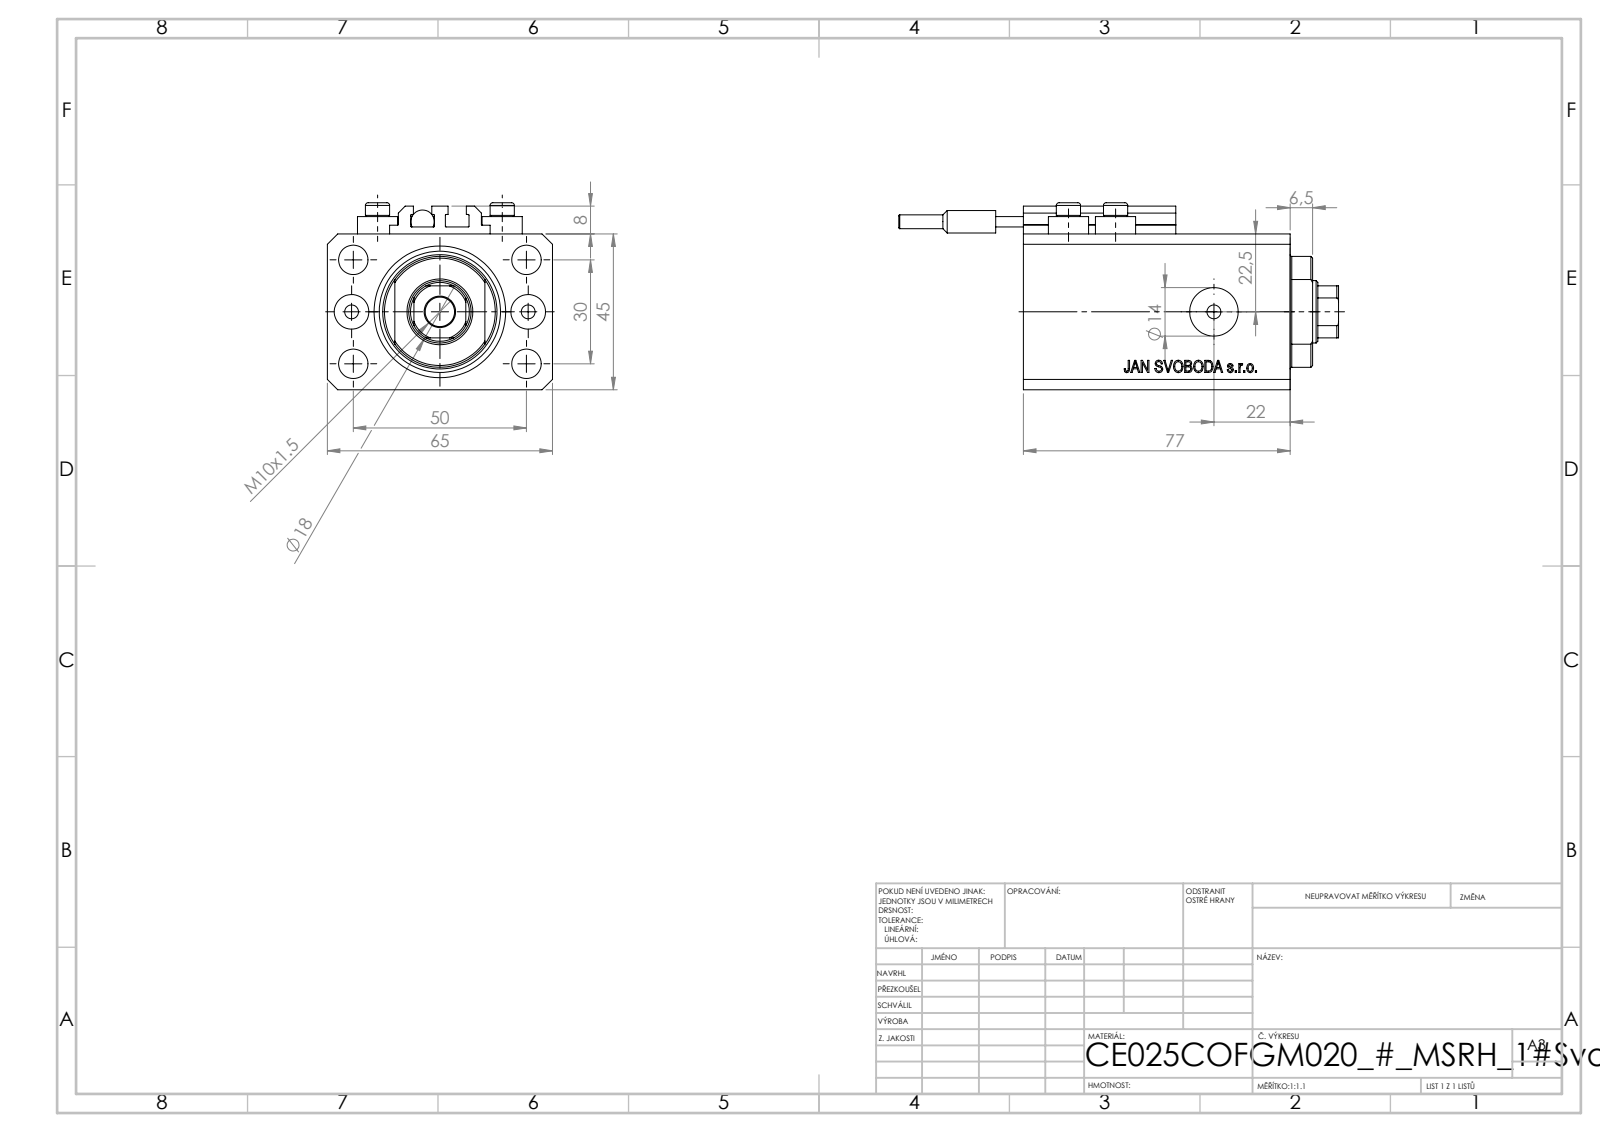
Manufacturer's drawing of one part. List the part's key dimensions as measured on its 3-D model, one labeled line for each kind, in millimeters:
Part name (STEP PRODUCT): V250CE_C_VCP; V250CE_VC_C; V250CE_C_Body; ALLEN BOLT V250CE (+1 more)
STEP written by: SolidWorks 2019 (CONFIG_CONTROL_DESIGN)
Units: millimetres
Bodies: 9 solids, 1060 faces (520 planar, 92 cylindrical, 448 other)
Overall size (bounding box): 127 × 65 × 54
Volume: 213 725 mm³ · Surface area: 58 641 mm²
Round holes (diameter × count): ⌀4 ×8, ⌀8.5 ×5, ⌀10 ×2, ⌀14 ×2, ⌀18 ×1, ⌀25 ×1, ⌀38 ×1
Round bosses / shafts (diameter × count): ⌀11.6 ×4, ⌀7 ×4, ⌀6.8 ×1, ⌀6.5 ×1, ⌀4 ×1
Partial cylindrical surfaces — rounded edges, fillets, slot ends (radius × count): R0.2 ×10, R8.5 ×1, R16 ×1
Main face-to-face distances: 45, 65, 14, 63, 77, 3, 47, 6.9, 56.1, 70.1
Hole centre spacings: 15.01, 29.15, 52.68, 13.6, 25.5, 30, 36, 38.48
